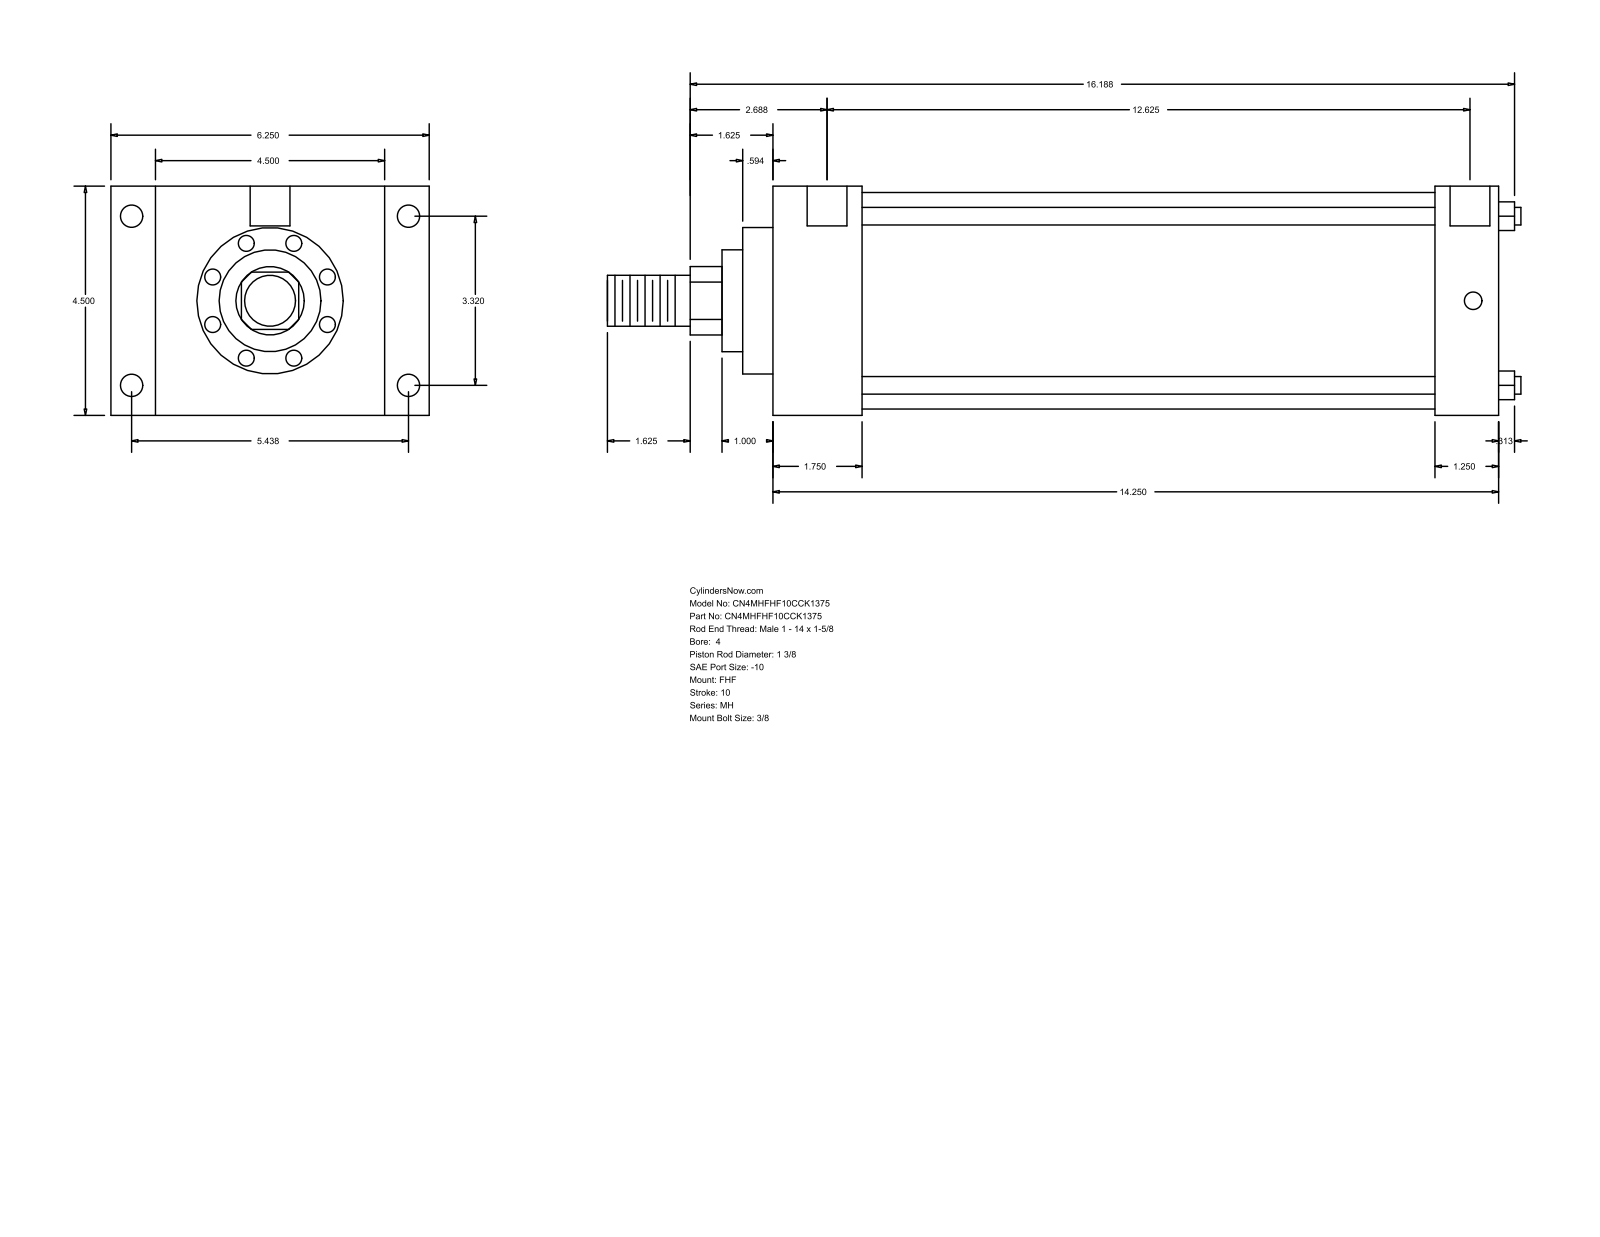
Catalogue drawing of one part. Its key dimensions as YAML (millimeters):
part_name: "MH_FHF__0400_1.375"
step_written_by: "GSSL Pune (CONFIG_CONTROL_DESIGN)"
units: millimeters
bodies: {solids: 0, faces: 90, planar: 61, cylindrical: 29, other: 0}
overall_size: [455.61, 158.75, 114.3]
round_holes:
  - {diameter: 8.73, count: 4}
  - {diameter: 11.13, count: 4}
  - {diameter: 19.84, count: 2}
round_bosses_or_shafts:
  - {diameter: 8.76, count: 4}
  - {diameter: 107.95, count: 1}
  - {diameter: 73.03, count: 1}
  - {diameter: 50.8, count: 1}
  - {diameter: 34.92, count: 1}
  - {diameter: 25.4, count: 1}
partial_cylinders:
  - {radius: 17.06, count: 1}
face_to_face_distances: [114.3, 361.96, 44.45, 317.51, 22.23, 136.53, 158.76, 330.21, 285.76, 31.75]
hole_center_spacings: [84.32, 138.12, 161.82, 323.85, 1.58, 1.59, 320.68, 322.26]
